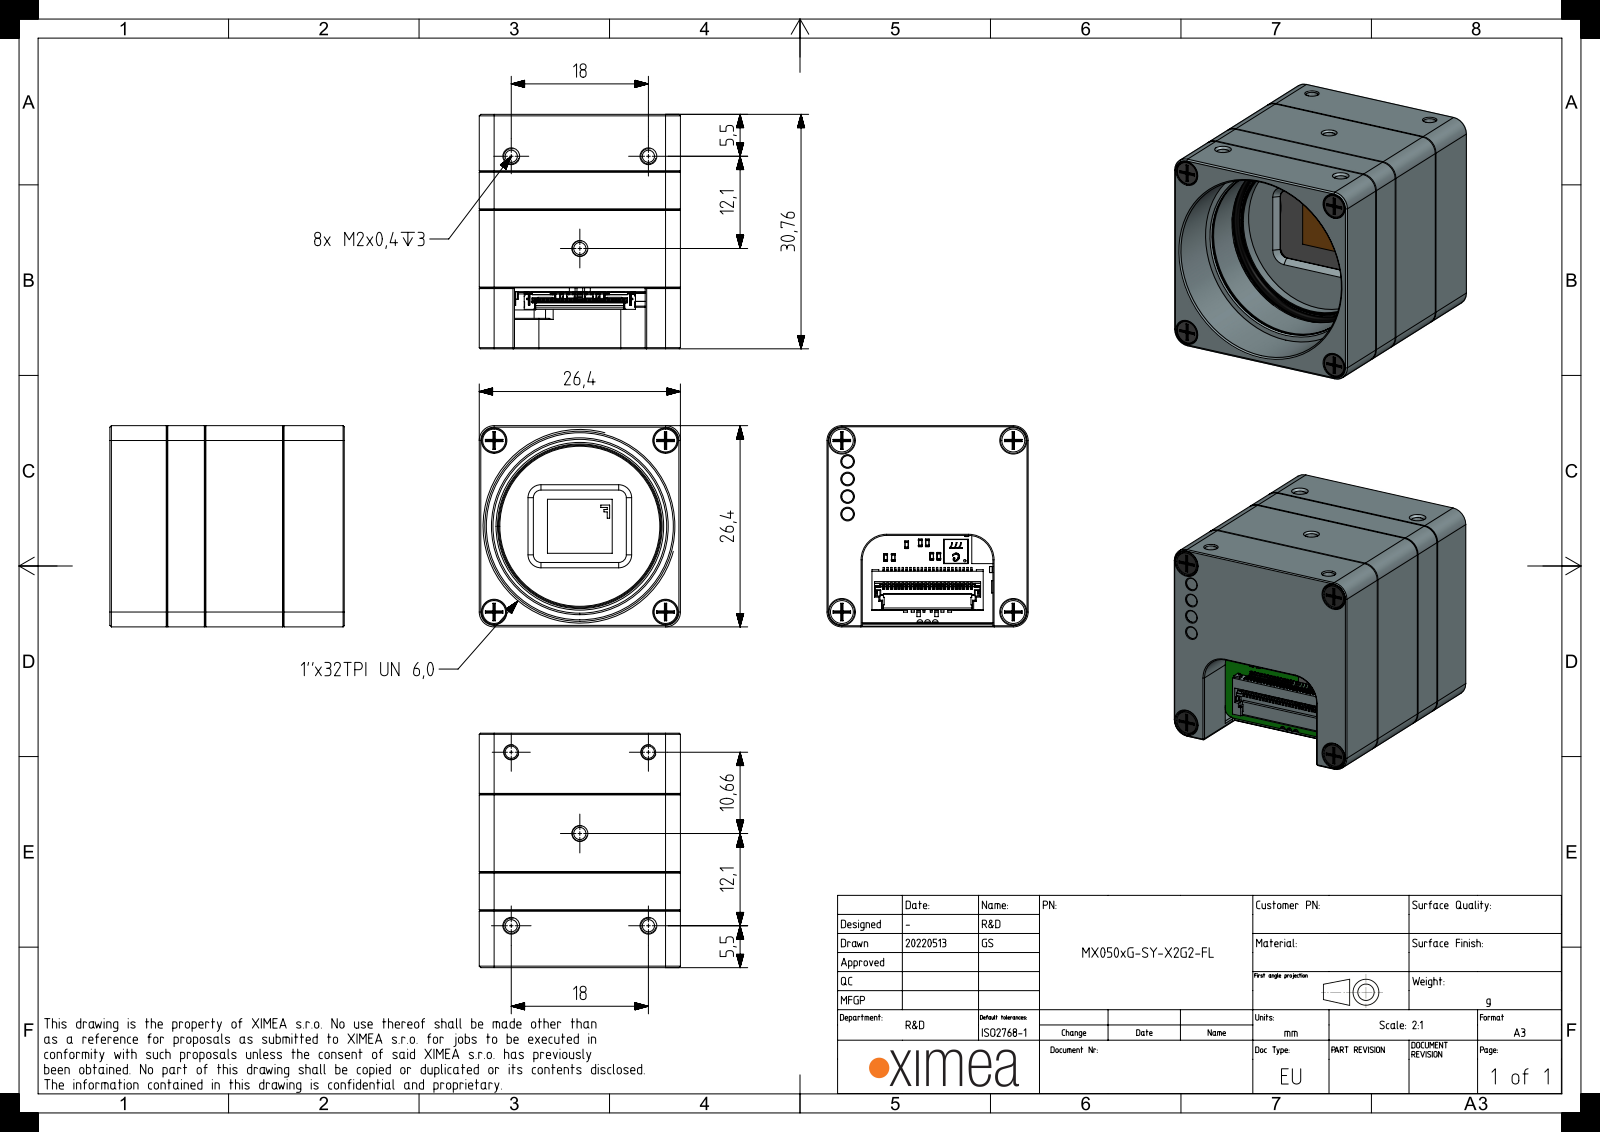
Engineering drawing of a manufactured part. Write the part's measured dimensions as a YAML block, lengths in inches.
part_name: "MX-X2G2-MAIN-FL-PCA; MECH-MX-THERMAL-PAD-10X10; SROB-M2x10-CUST; MECH-LIGHTPIPE-1.63x4.14 (+8 more)"
step_written_by: "SIEMENS PLM Software NX 1907 (AUTOMOTIVE_DESIGN)"
units: inches
bodies: {solids: 32, faces: 7540, planar: 5180, cylindrical: 2089, other: 271}
overall_size: [1.211, 1.039, 1.039]
volume: 0.629
surface_area: 26.32
round_holes:
  - {diameter: 0.063, count: 13}
  - {diameter: 0.035, count: 4}
  - {diameter: 0.071, count: 4}
  - {diameter: 0.079, count: 4}
  - {diameter: 0.083, count: 4}
  - {diameter: 0.118, count: 4}
  - {diameter: 0.126, count: 4}
  - {diameter: 0.132, count: 4}
  - {diameter: 0.051, count: 2}
  - {diameter: 0.073, count: 1}
  - {diameter: 0.073, count: 1}
  - {diameter: 0.827, count: 1}
round_bosses_or_shafts:
  - {diameter: 0.075, count: 4}
  - {diameter: 0.064, count: 4}
  - {diameter: 0.033, count: 4}
  - {diameter: 0.118, count: 2}
  - {diameter: 0.063, count: 2}
  - {diameter: 0.984, count: 1}
  - {diameter: 0.85, count: 1}
partial_cylinders:
  - {radius: 0.059, count: 19}
  - {radius: 0.013, count: 17}
  - {radius: 0.004, count: 14}
  - {radius: 0.006, count: 14}
  - {radius: 0.039, count: 14}
  - {radius: 0.015, count: 12}
  - {radius: 0.008, count: 10}
  - {radius: 0.051, count: 8}
face_to_face_distances: [0.039, 1.039, 0.138, 0.447, 0.27, 0.304, 0.165, 0.178, 0.266, 0.408]
hole_center_spacings: [0.15, 0.508, 0.626, 0.739, 0.869, 0.886, 1.131, 0.091]
